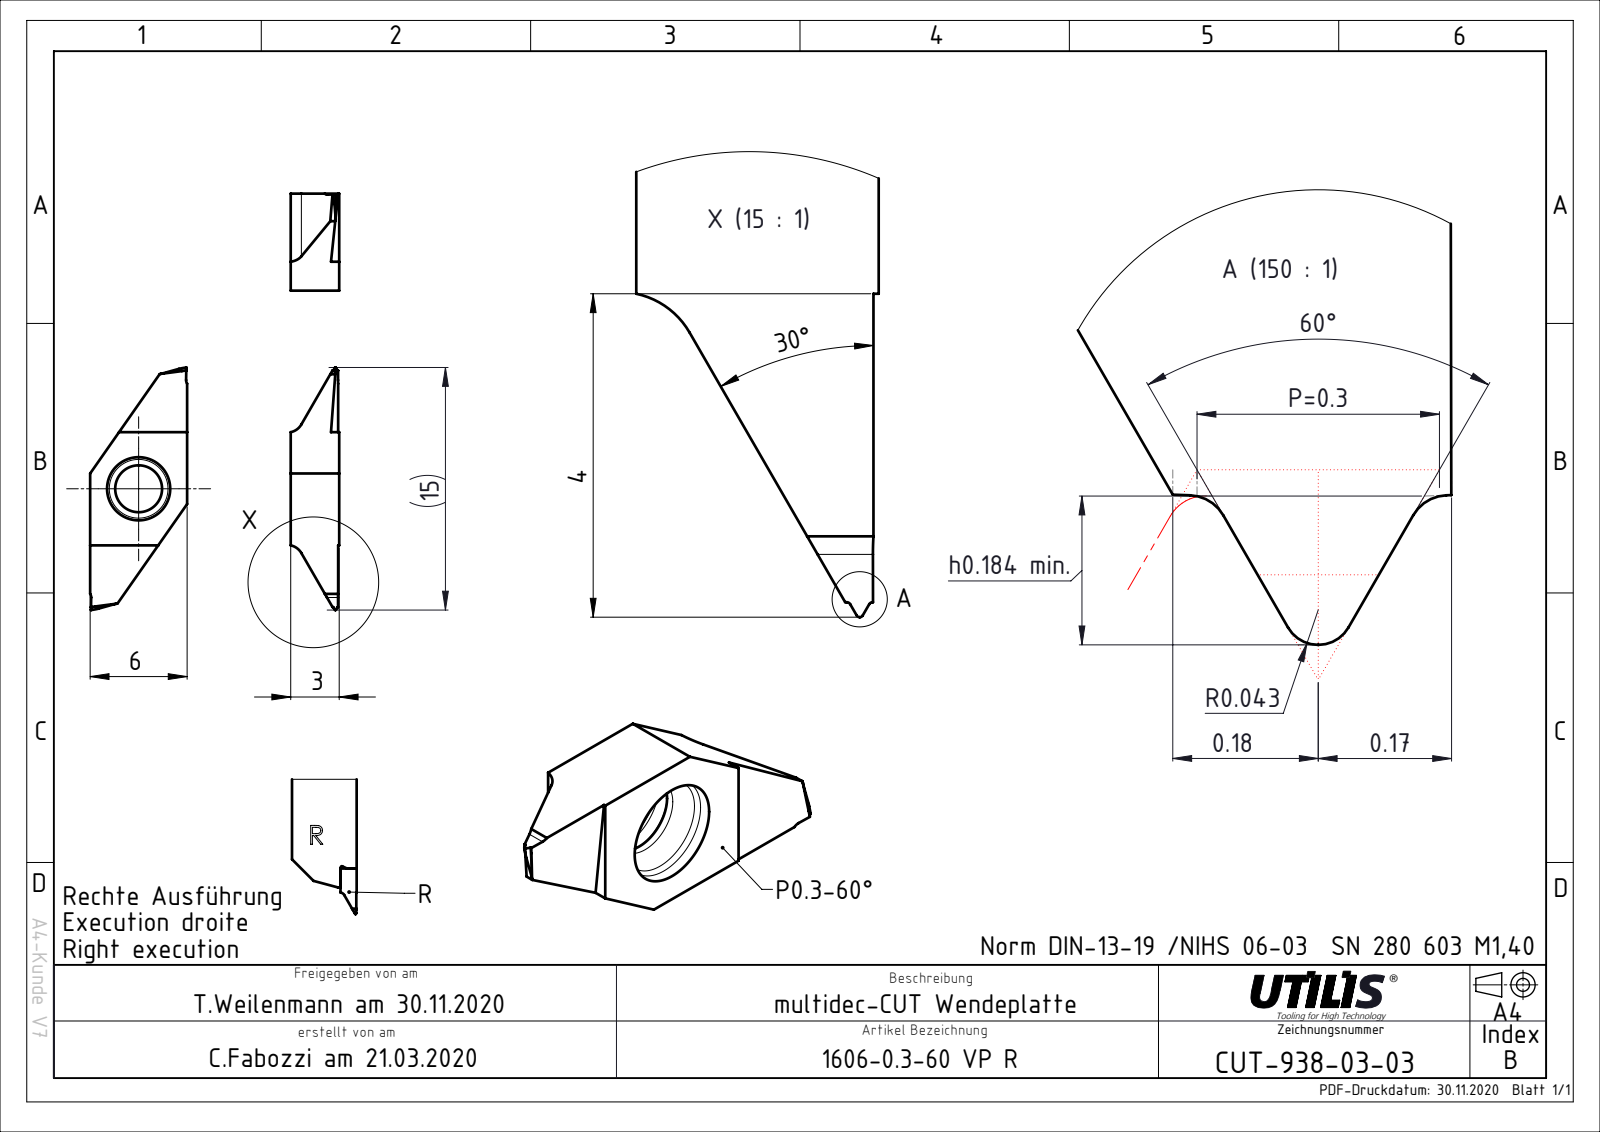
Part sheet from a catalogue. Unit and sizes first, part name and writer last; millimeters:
Units: millimetres
Overall size (bounding box): 15 × 6 × 3
Round holes (diameter × count): ⌀2.9 ×1
Partial cylindrical surfaces — rounded edges, fillets, slot ends (radius × count): R1 ×2
Main face-to-face distances: 6, 3, 9, 12, 11.15, 7, 13.15
Volume: 128 mm³ · Surface area: 211 mm²
Bodies: 1 solid, 40 faces (22 planar, 14 cylindrical, 4 other)
Part name (STEP PRODUCT): CUT-938-03; ASME Y14.5
STEP written by: FormatWorks Professional (AP242_MANAGED_MODEL_BASED_3D_ENGINEERING_MIM_LF)
